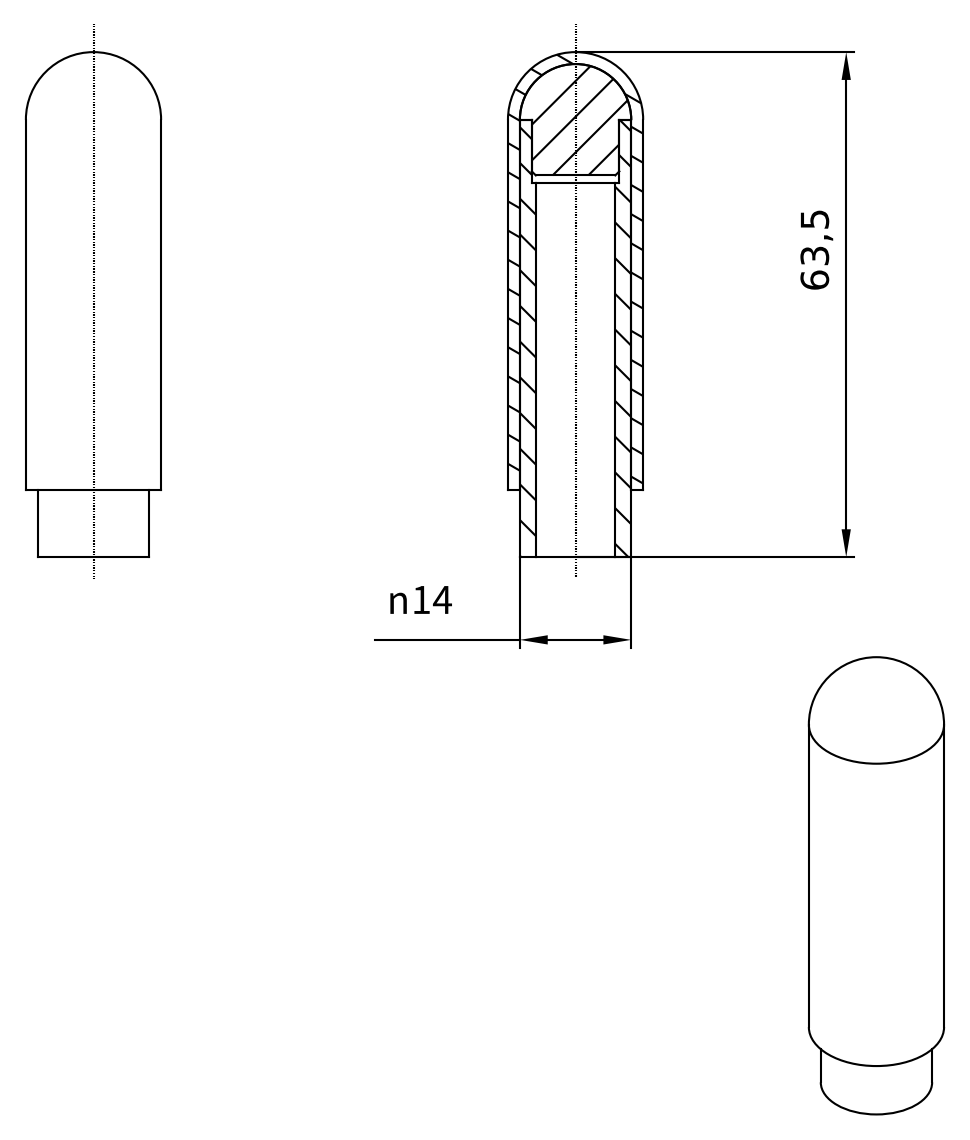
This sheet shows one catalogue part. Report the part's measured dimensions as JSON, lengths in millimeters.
{"step_written_by": "Autodesk Inventor 8 (AUTOMOTIVE_DESIGN)", "units": "millimeters", "bodies": {"solids": 1, "faces": 16, "planar": 4, "cylindrical": 8, "other": 4}, "overall_size": [63.5, 17, 17], "volume_mm3": 9359, "surface_area_mm2": 5106, "round_holes": [[10, 1], [11, 1]], "round_bosses_or_shafts": [[17, 1], [14, 1]], "face_to_face_distances": [48, 8.5, 39.5, 47, 38.5, 1]}
